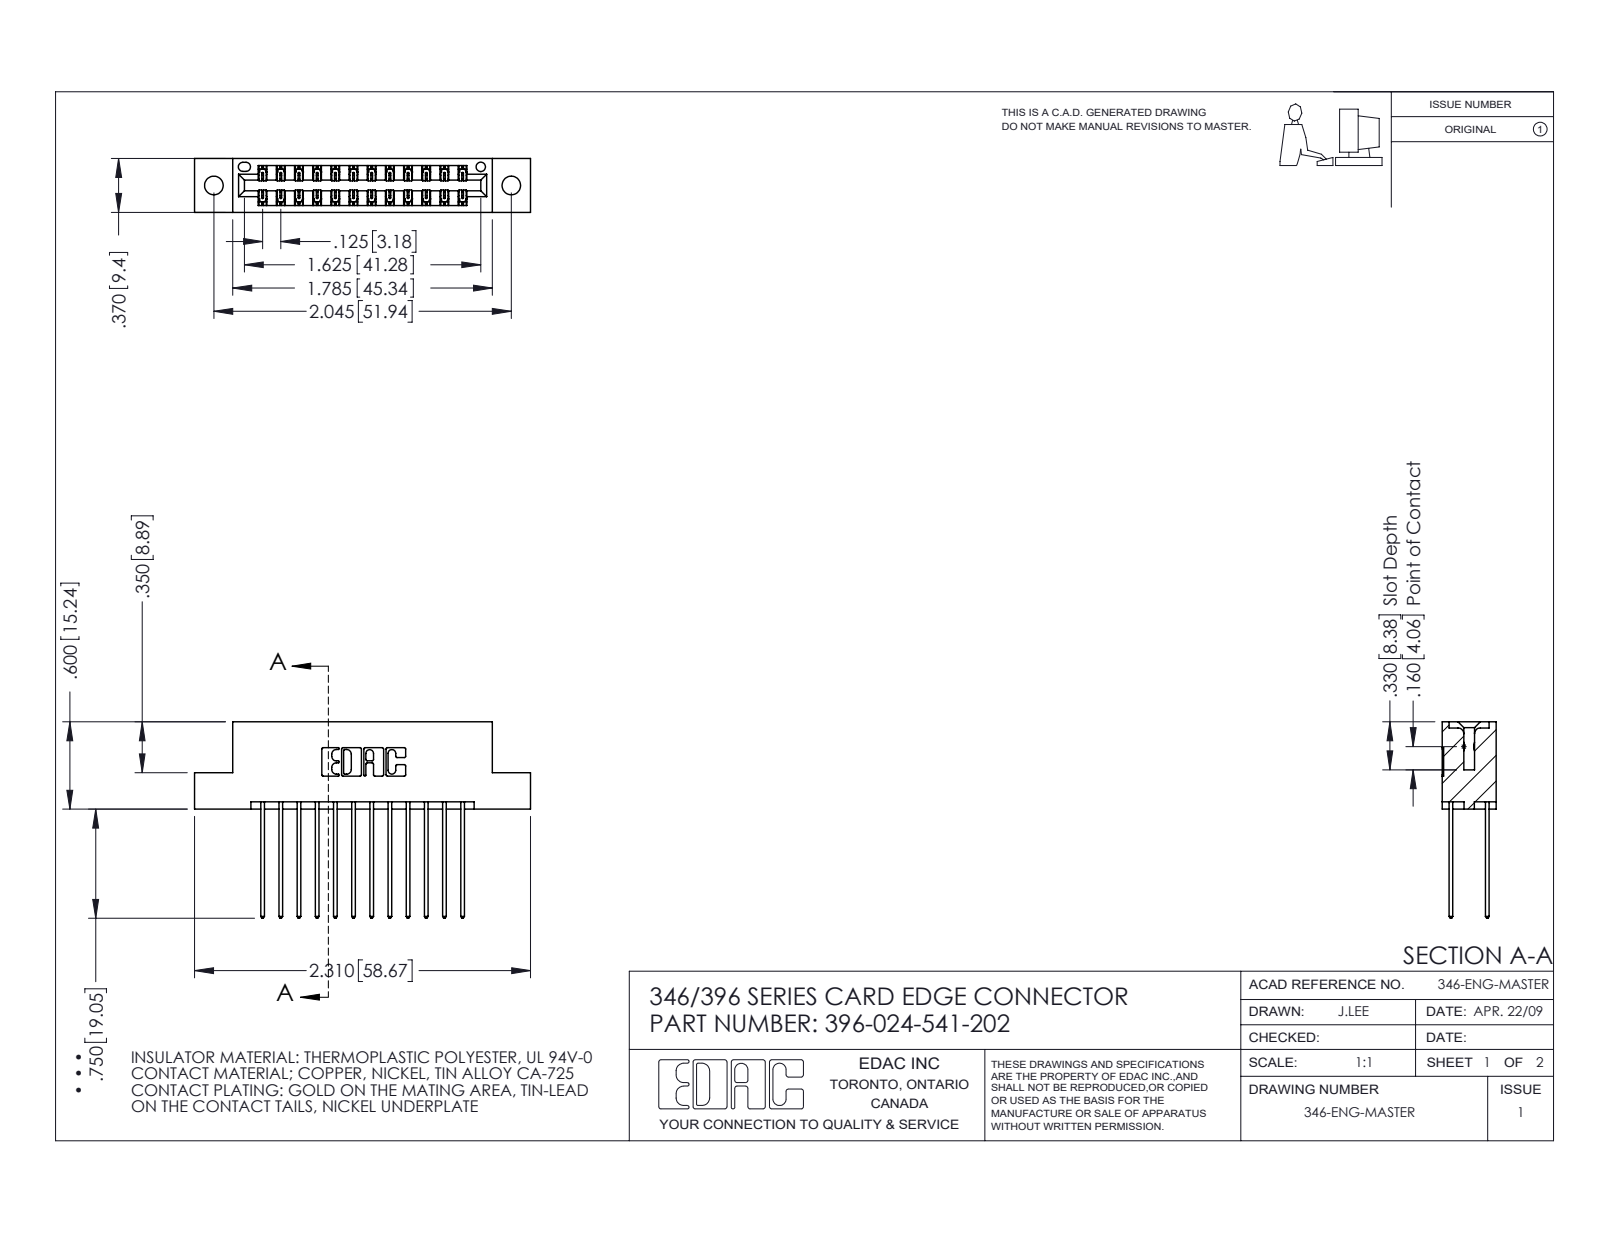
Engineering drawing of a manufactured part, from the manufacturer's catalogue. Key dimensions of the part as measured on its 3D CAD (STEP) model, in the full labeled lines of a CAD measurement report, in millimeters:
Part name (STEP PRODUCT): 345-292-001_345-293-141; 396-024-541-202; 346 Part_Flush Mounting Lugs - 0.128 Dia
STEP written by: SolidWorks 2016 (CONFIG_CONTROL_DESIGN)
Units: millimetres
Bodies: 25 solids, 1370 faces (916 planar, 454 cylindrical, 0 other)
Overall size (bounding box): 58.7 × 34.3 × 9.4
Volume: 5 590 mm³ · Surface area: 7 600 mm²
Round holes (diameter × count): ⌀3.3 ×2, ⌀1.6 ×1
Partial cylindrical surfaces — rounded edges, fillets, slot ends (radius × count): R0.2 ×36, R0.3 ×24, R0.3 ×22, R0.2 ×6, R0.8 ×6, R0.7 ×3, R0.4 ×2, R0.6 ×2
Main face-to-face distances: 6.4, 1.2, 8.2, 1.8, 7.6, 0.6, 9.4, 7, 3.8, 5.6
Hole centre spacings: 6.2, 46.7, 51.9
